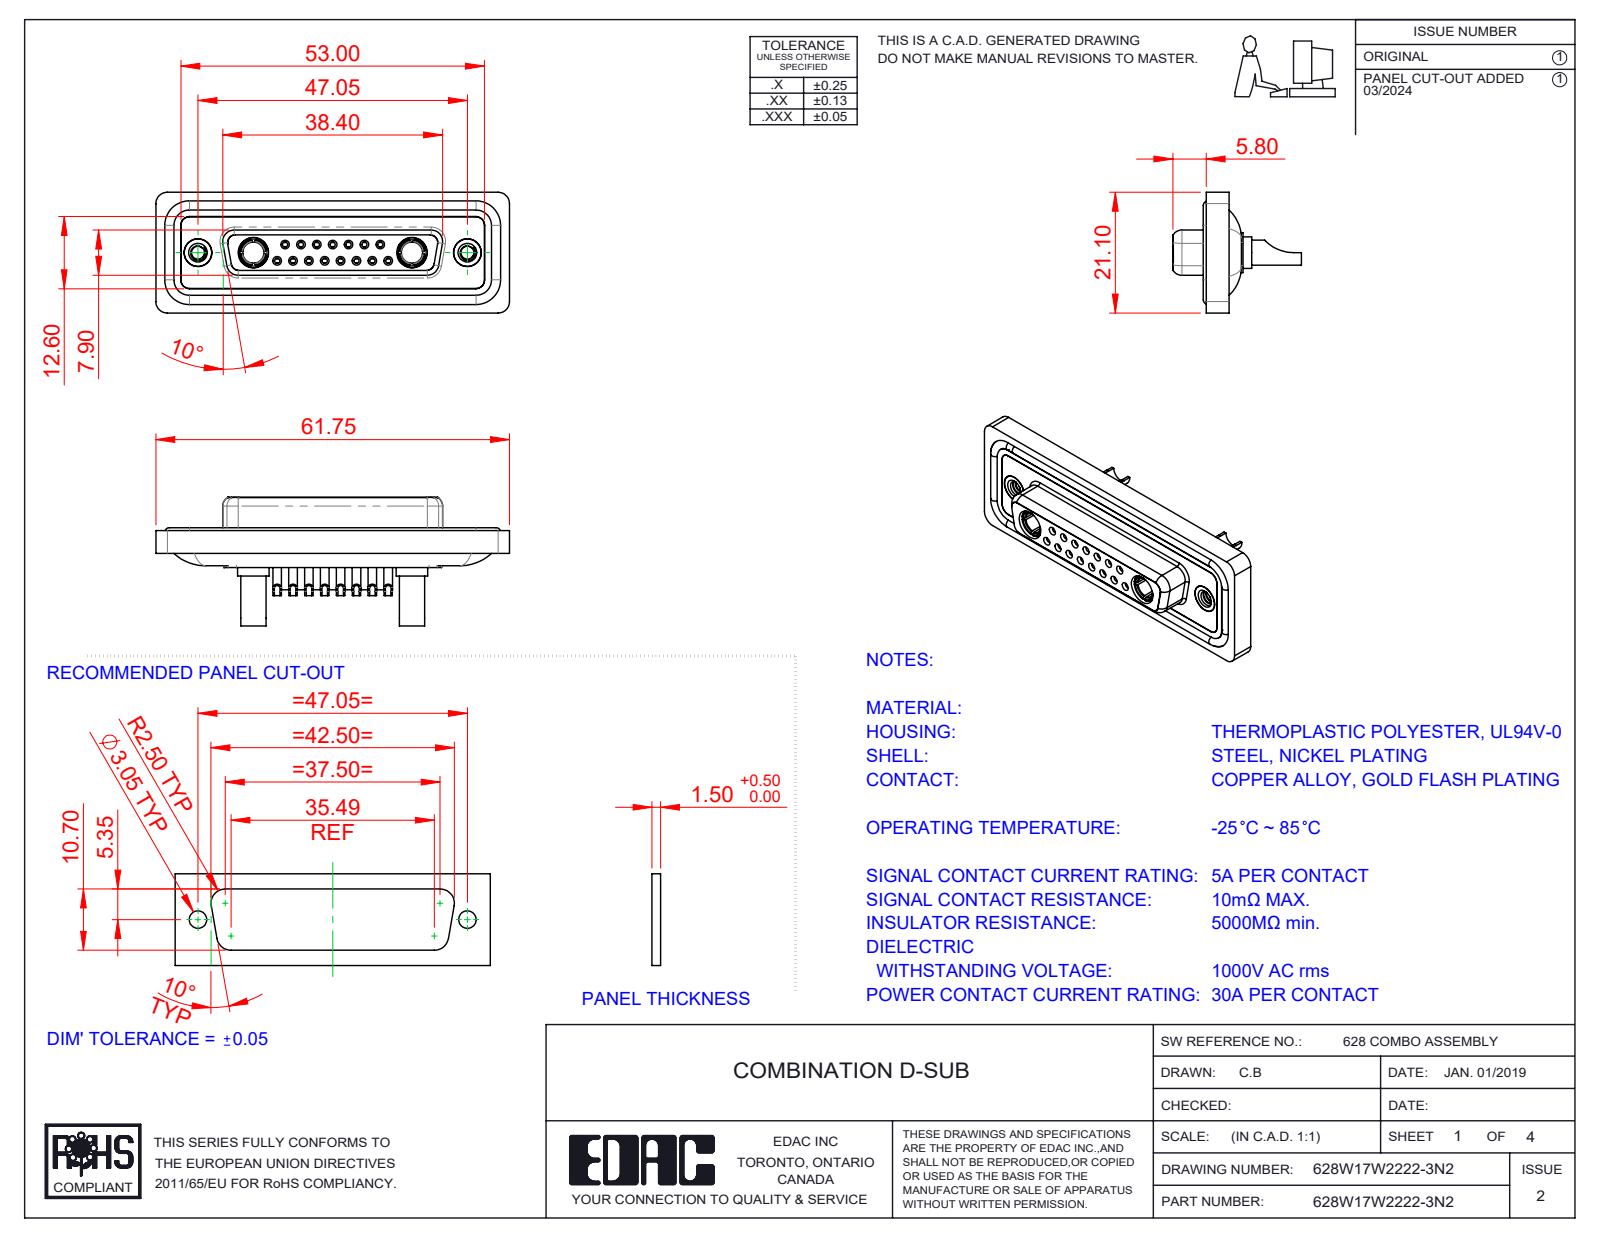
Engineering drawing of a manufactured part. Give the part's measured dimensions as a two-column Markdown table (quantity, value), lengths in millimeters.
| quantity | value |
| --- | --- |
| part name | 628Combo Contact Row 2_22; 628Combo Shell Rear_25 Contacts; 628Combo Threaded Rivet_2; 628Combo Housing_17W2 (+5 more) |
| STEP written by | SolidWorks 2023 (CONFIG_CONTROL_DESIGN) |
| units | millimeters |
| bodies | 26 solids, 1371 faces (424 planar, 555 cylindrical, 392 other) |
| overall size | 61.75 × 22.45 × 21.1 |
| volume | 8 403 mm³ |
| surface area | 14 230 mm² |
| round holes (diameter × count) | 0.9 × 15, 1 × 15, 1.1 × 15, 1.5 × 15, 2 × 15, 1.6 × 8, 1.7 × 7, 4.85 × 4, 2.26 × 2, 3.5 × 2, 3.7 × 2, 4 × 2 |
| round bosses / shafts (diameter × count) | 2.2 × 15, 1.6 × 11, 5.5 × 2, 5.2 × 2, 4.96 × 2, 4.95 × 2, 4.8 × 2, 4.75 × 2 |
| partial cylindrical surfaces (radius × count) | 1.5 × 22, 2 × 18, 1.35 × 8, 1.6 × 8, 1 × 6, 0.25 × 4, 0.5 × 4, 0.6 × 4 |
| main face-to-face distances | 0.4, 1.8, 7.45, 5.65, 6.6, 0.5, 7.05, 1.6, 2.9, 1.1 |
| hole center spacings | 3.16, 2.77, 8.31, 5.54, 5.03, 5.04, 7.49, 11.08 |
